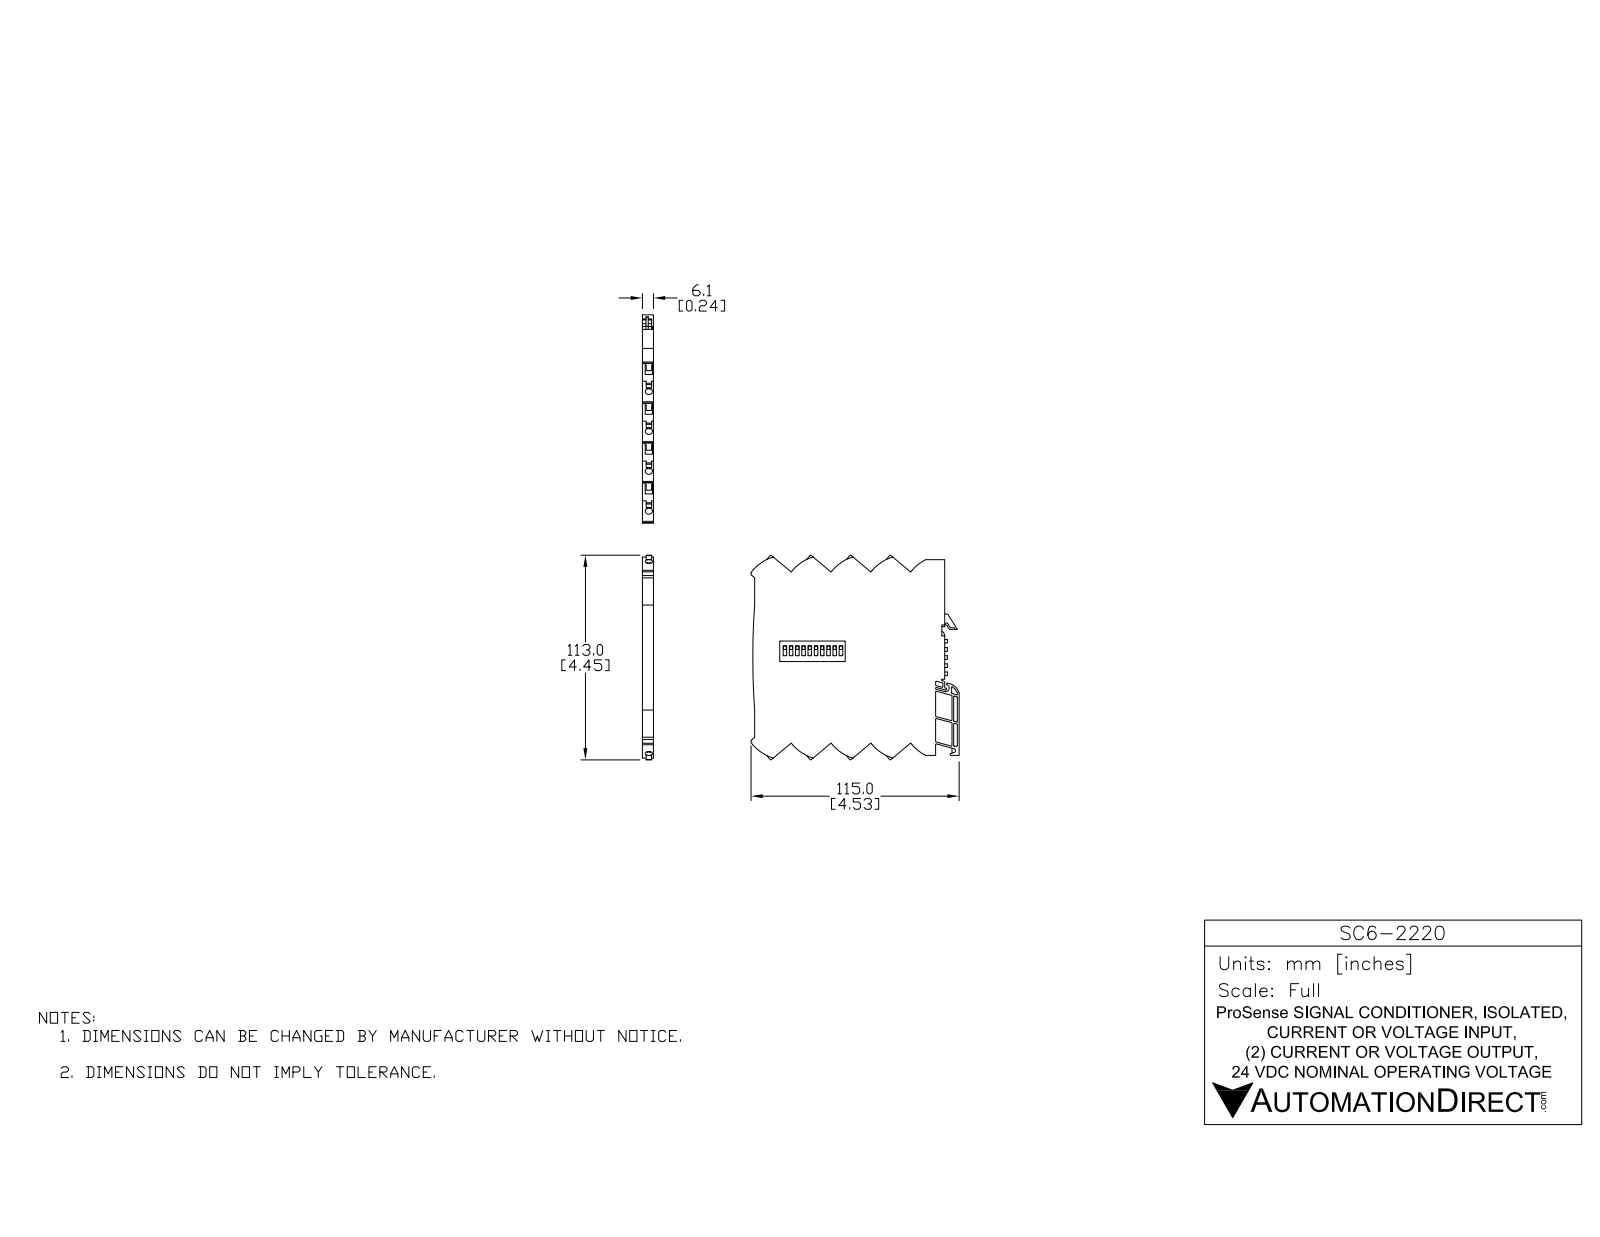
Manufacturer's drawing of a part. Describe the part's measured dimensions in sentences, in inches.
The part is named "SC6-2220". Its 3-D file was written by "SolidWorks 2017 (AUTOMOTIVE_DESIGN)". It is 1 solid with 644 faces: 443 planar, 117 cylindrical and 84 other. Overall it measures 4.528 by 4.448 by 0.24 inches. Its volume is 3.953 cubic inches and its surface area 43.93 square inches. Round holes: 8 of diameter 0.157. Partial cylindrical surfaces (rounded edges, fillets, slot ends): 33 of radius 0.012, 10 of radius 0.02, 10 of radius 0.059, 10 of radius 0.918, 2 of radius 0.008, 1 of radius 0.022, 1 of radius 0.043, 1 of radius 0.058. The main face-to-face distances are 0.24, 0.039, 0.118, 0.157, 0.081, 0.12, 0.201, 0.557, 0.041, 0.159. The hole center spacings are 0.557, 1.113, 0.557, 1.67.
